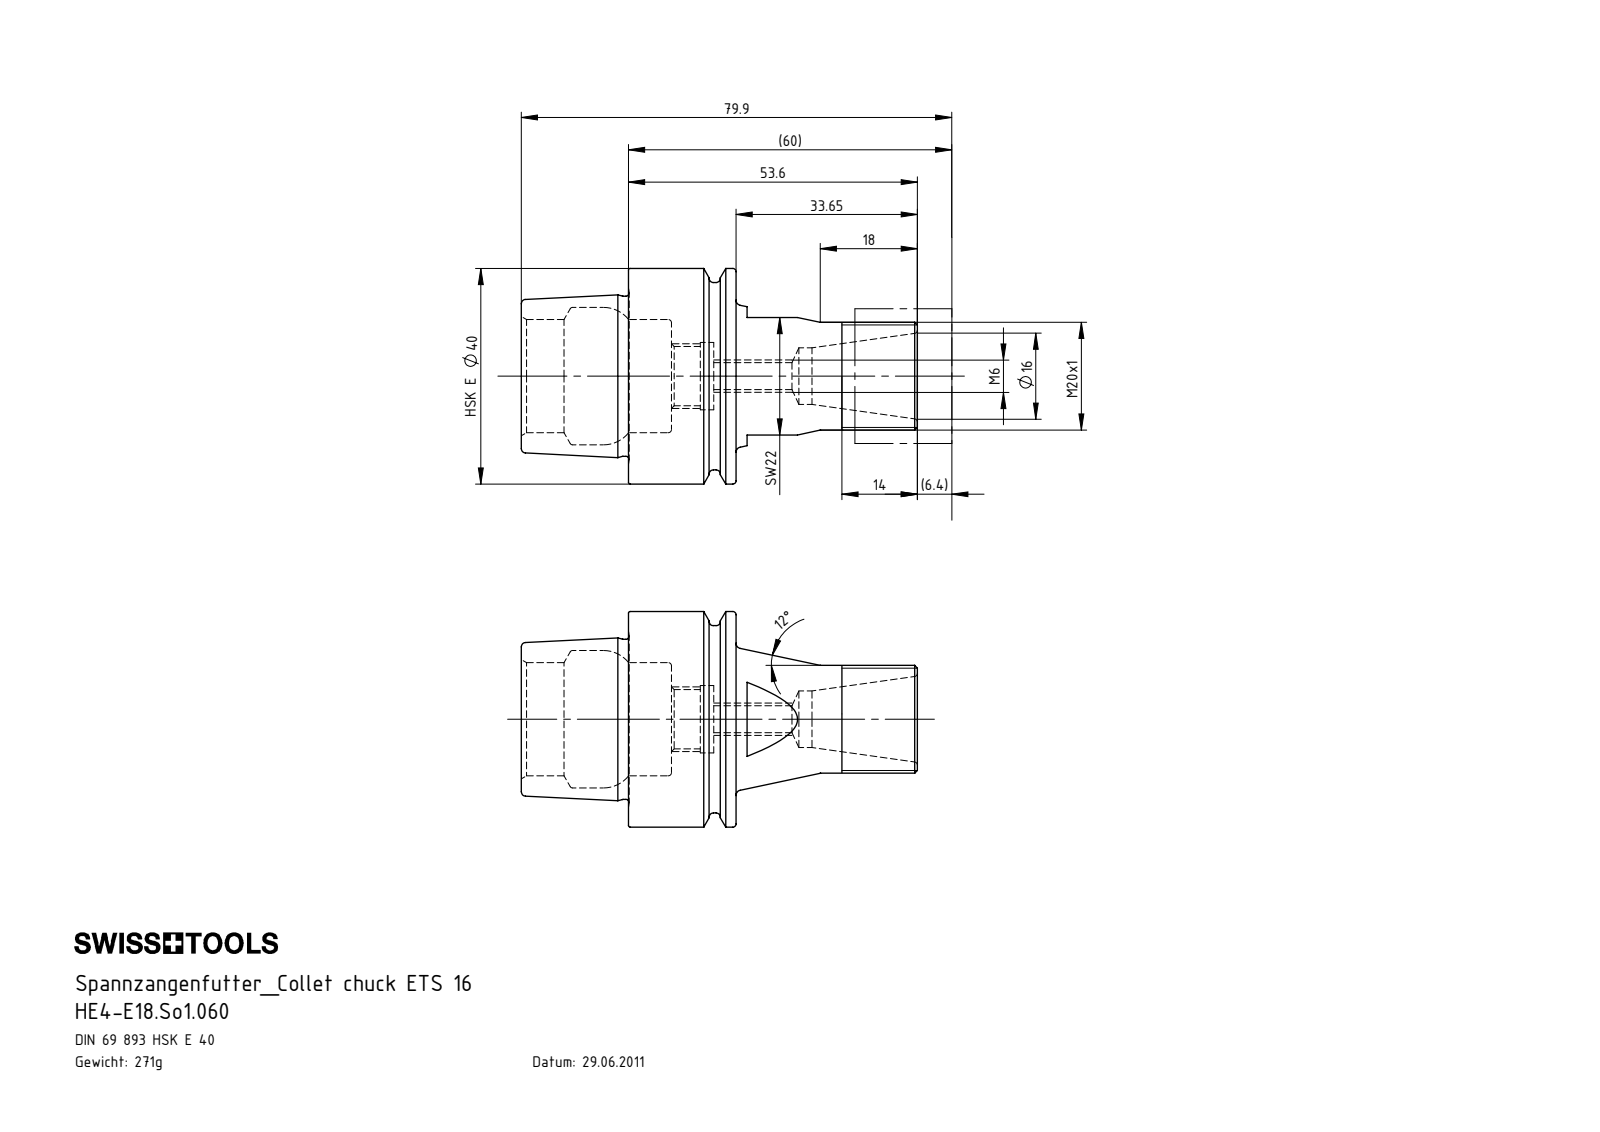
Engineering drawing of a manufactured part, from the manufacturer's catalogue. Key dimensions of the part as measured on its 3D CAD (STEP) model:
Part name (STEP PRODUCT): HE4-E18.So1.060; HE4-E18.So1.060_B_Fertigbearbeitung
STEP written by: SolidWorks 2015 (AUTOMOTIVE_DESIGN)
Units: millimetres
Bodies: 1 solid, 87 faces (13 planar, 24 cylindrical, 50 other)
Overall size (bounding box): 73.5 × 40 × 40
Volume: 33 726 mm³ · Surface area: 12 675 mm²
Round holes (diameter × count): ⌀5 ×1, ⌀10.5 ×1, ⌀11 ×1, ⌀12.5 ×1, ⌀21 ×1, ⌀25.5 ×1
Round bosses / shafts (diameter × count): ⌀40 ×1, ⌀34.75 ×1, ⌀29.71 ×1, ⌀20 ×1
Main face-to-face distances: 19.95, 7.95, 12, 19.9, 27.85, 39.85, 35.7, 15.8, 7.85, 4.15
